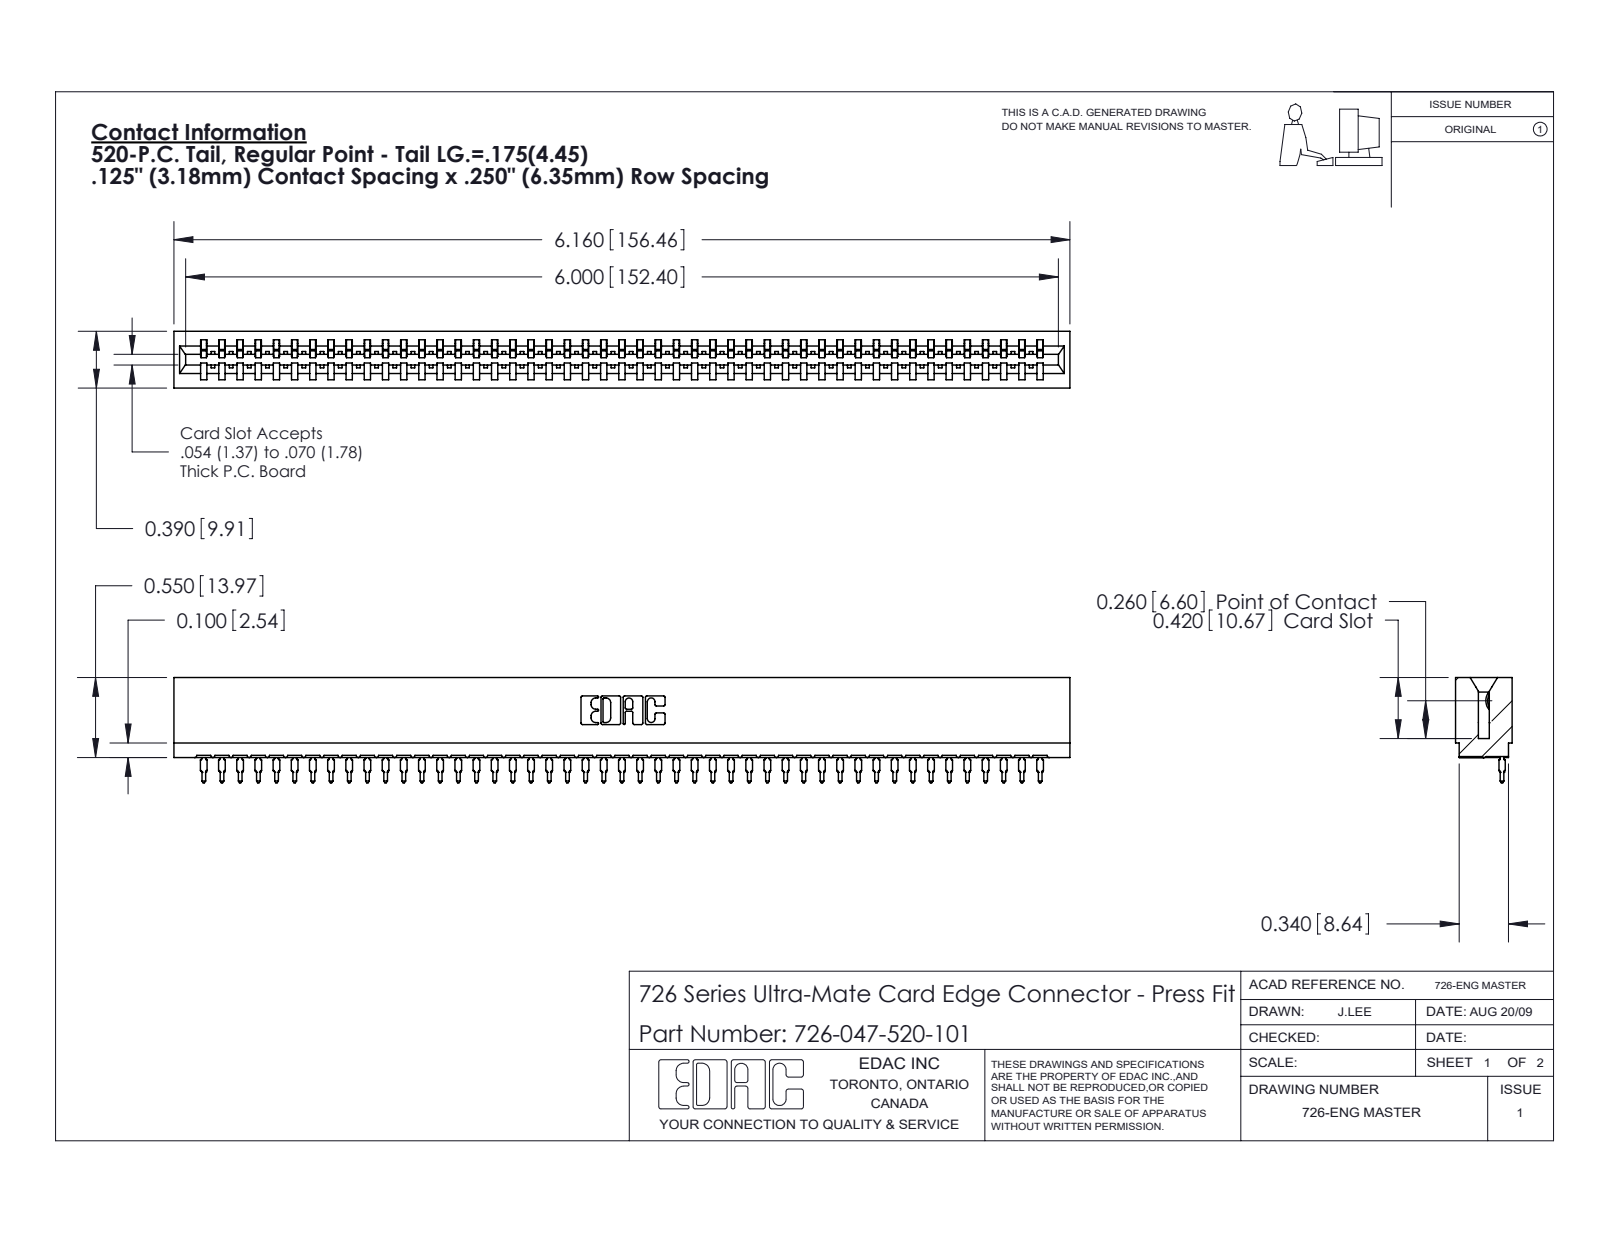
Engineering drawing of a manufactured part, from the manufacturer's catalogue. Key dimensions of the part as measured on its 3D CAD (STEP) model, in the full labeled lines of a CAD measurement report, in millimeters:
Part name (STEP PRODUCT): 726 Part_.515 Slot Depth - 01; 726-047-520-101; 746-292-001_520
STEP written by: SolidWorks 2020 (CONFIG_CONTROL_DESIGN)
Units: millimetres
Bodies: 48 solids, 5173 faces (3016 planar, 935 cylindrical, 1222 other)
Overall size (bounding box): 156.5 × 18.4 × 9.9
Volume: 13 900 mm³ · Surface area: 20 920 mm²
Partial cylindrical surfaces — rounded edges, fillets, slot ends (radius × count): R0.5 ×94, R0.4 ×48, R0.3 ×22, R0.2 ×6, R0.8 ×6, R0.1 ×4, R0.3 ×4, R0.7 ×3
Main face-to-face distances: 1.4, 8.5, 9.9, 0.6, 7.8, 6.4, 7, 9.3, 0.8, 4.4
